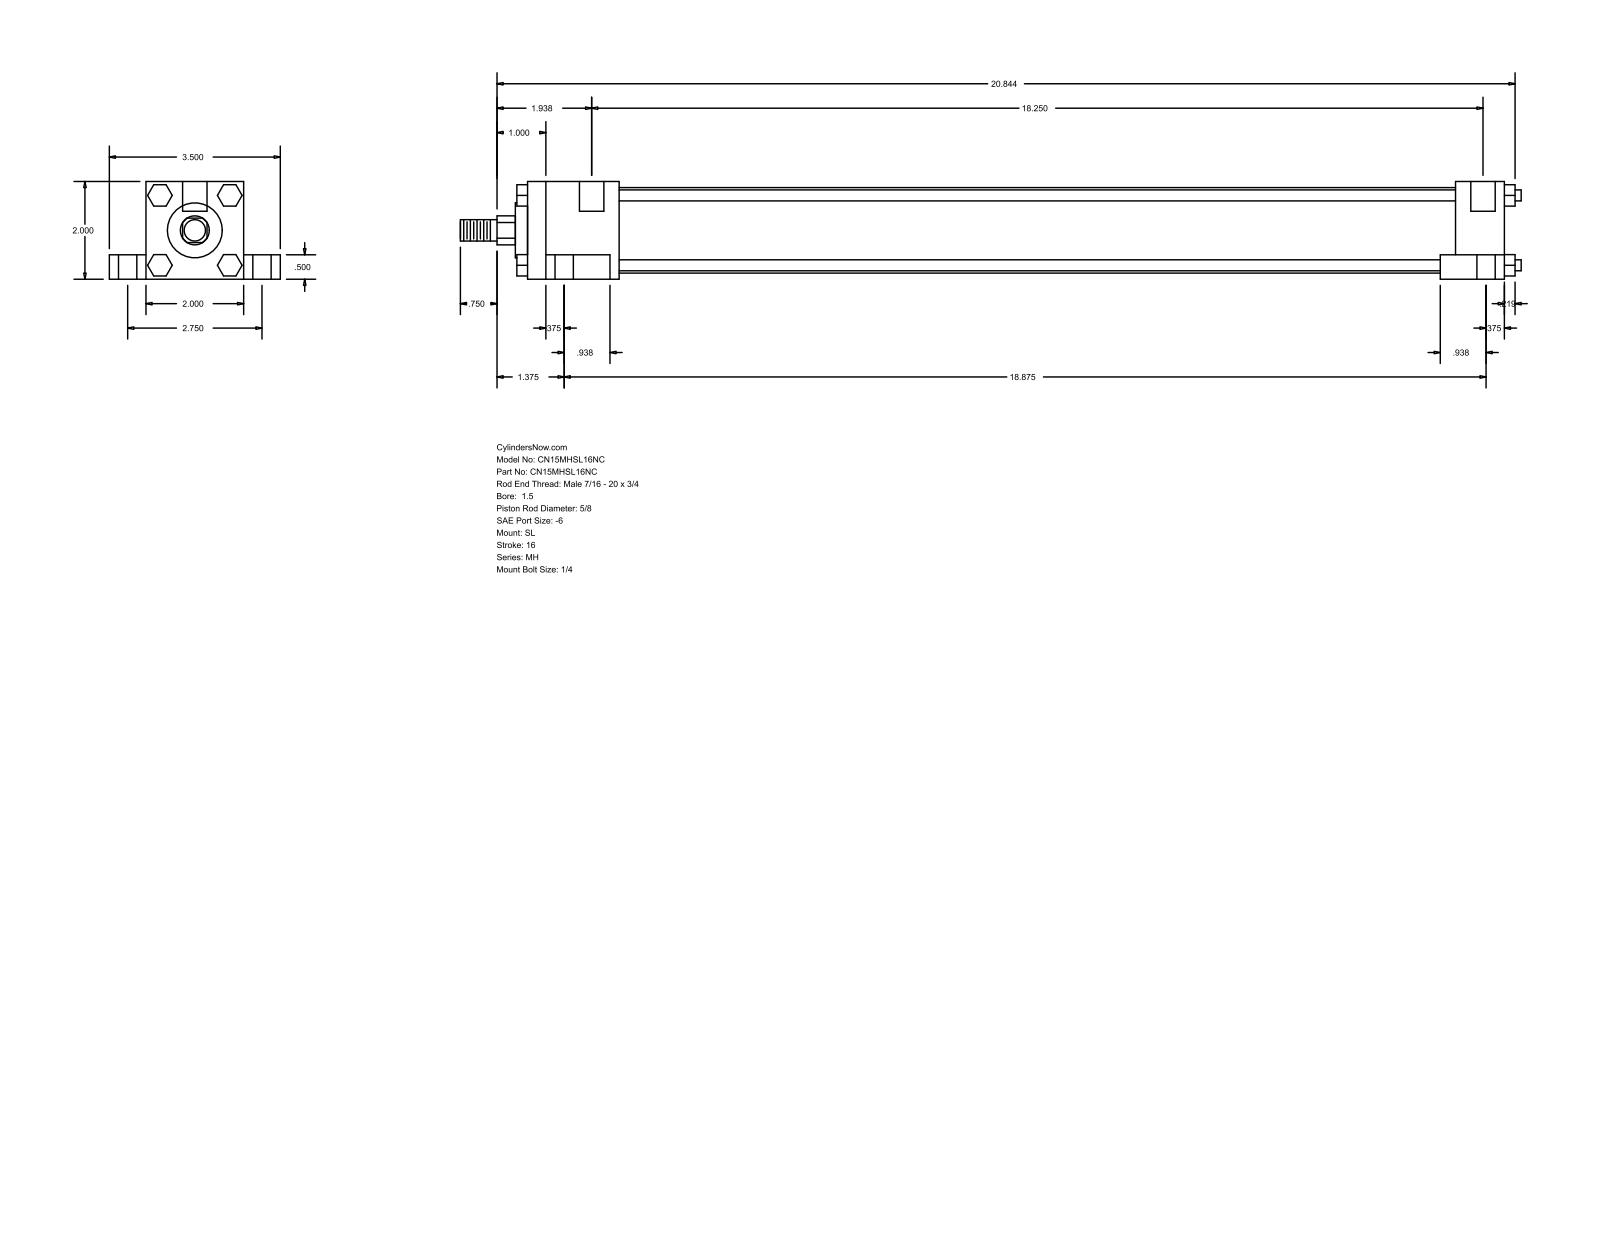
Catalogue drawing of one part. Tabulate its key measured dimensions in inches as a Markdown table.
| quantity | value |
| --- | --- |
| part name | MH_SL__0150_0.625 |
| STEP written by | GSSL Pune (CONFIG_CONTROL_DESIGN) |
| units | inches |
| bodies | 0 solids, 148 faces (112 planar, 36 cylindrical, 0 other) |
| overall size | 21.719 × 3.5 × 2 |
| round holes (diameter × count) | 0.219 × 4, 0.375 × 4, 0.625 × 4, 0.5 × 2 |
| round bosses / shafts (diameter × count) | 0.225 × 4, 1.75 × 1, 1.125 × 1, 0.625 × 1, 0.437 × 1 |
| partial cylindrical surfaces (radius × count) | 0.297 × 1 |
| main face-to-face distances | 2, 1.5, 0.75, 0.5, 2.75, 20, 1, 0.375, 1.313, 18.313 |
| hole center spacings | 1.376, 1.443, 1.485, 2.75, 18.364, 18.375, 18.489, 18.863 |
